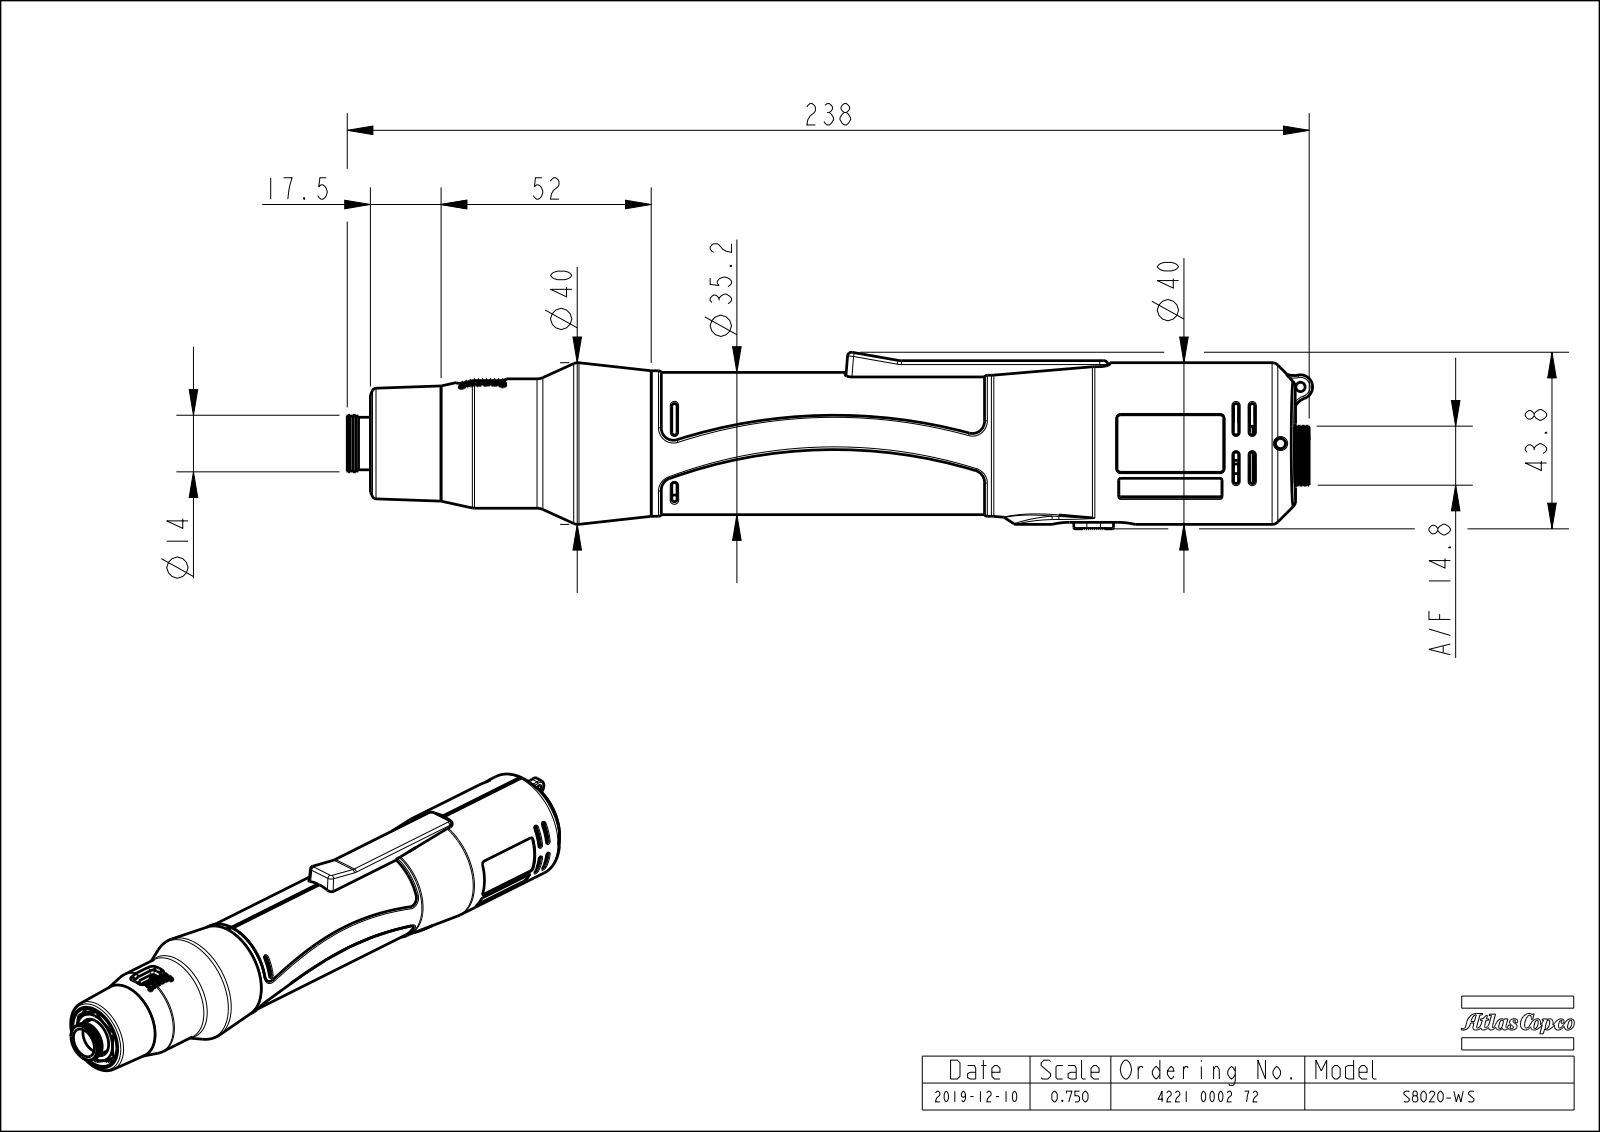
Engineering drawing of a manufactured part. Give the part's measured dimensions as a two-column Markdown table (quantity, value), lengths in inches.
| quantity | value |
| --- | --- |
| part name | EXT_COMP_SW0068; 4221000418; 4221000403; 4221000272_DIM_ASM |
| STEP written by | CREO PARAMETRIC BY PTC INC, 2018100 (AP242_MANAGED_MODEL_BASED_3D_ENGINEERING_MIM_LF) |
| units | inches |
| bodies | 9 solids, 3196 faces (1388 planar, 806 cylindrical, 1002 other) |
| overall size | 9.407 × 1.72 × 1.575 |
| volume | 7.516 in³ |
| surface area | 135.4 in² |
| round holes (diameter × count) | 0.083 × 4, 0.11 × 4, 0.161 × 4, 0.059 × 3, 0.079 × 2, 0.081 × 1, 0.433 × 1, 0.512 × 1, 0.571 × 1, 0.622 × 1, 0.803 × 1, 0.906 × 1 |
| round bosses / shafts (diameter × count) | 0.157 × 8, 0.093 × 5, 0.079 × 5, 0.189 × 4, 0.091 × 2, 1.575 × 1, 1.417 × 1, 1.386 × 1 |
| partial cylindrical surfaces (radius × count) | 0.02 × 112, 0.039 × 76, 0.059 × 26, 7.254 × 16, 0.012 × 13, 0.197 × 13, 0.018 × 9, 0.157 × 8 |
| main face-to-face distances | 0.079, 0.039, 0.197, 0.228, 0.059, 3.461, 0.071, 0.118, 1.272, 0.689 |
| hole center spacings | 2.03, 2.276, 0.118, 0.252, 0.298, 0.662, 0.832, 0.897 |
